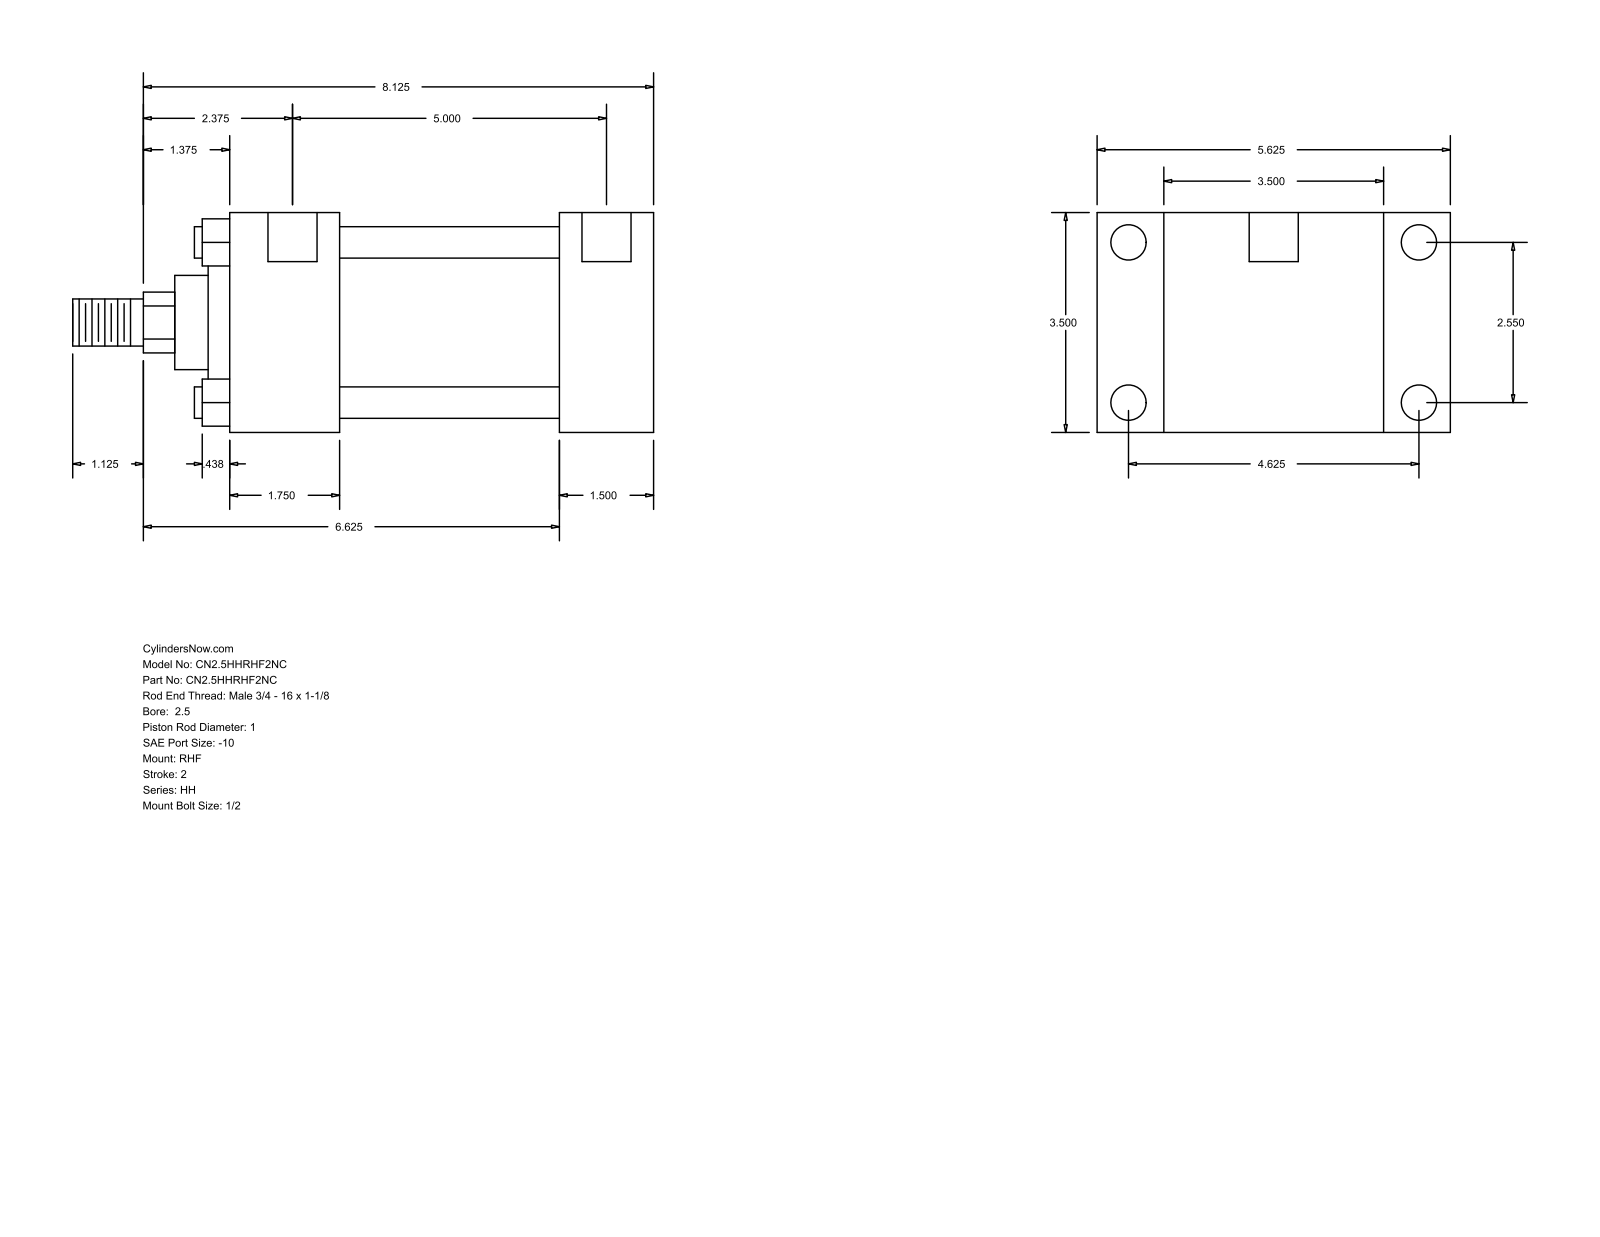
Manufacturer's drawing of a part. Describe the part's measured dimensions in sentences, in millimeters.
The part is named "HH_RHF__0250_1". Its 3-D file was written by "GSSL Pune (CONFIG_CONTROL_DESIGN)". It is 0 solids with 90 faces: 61 planar, 29 cylindrical and 0 other. Overall it measures 234.95 by 142.88 by 88.9 millimeters. Round holes: 4 of diameter 5.56, 4 of diameter 14.3, 2 of diameter 19.84. Round bosses or shafts: 4 of diameter 12.7, 1 of diameter 73.03, 1 of diameter 60.33, 1 of diameter 38.1, 1 of diameter 25.4, 1 of diameter 19.05. Partial cylindrical surfaces (rounded edges, fillets, slot ends): 1 of radius 12.29. The main face-to-face distances are 88.9, 38.1, 26.99, 115.89, 133.36, 171.46, 142.88, 44.46, 127, 8.73. The hole center spacings are 1.59, 64.76, 117.48, 128.58, 130.17, 134.15, 126.99.
